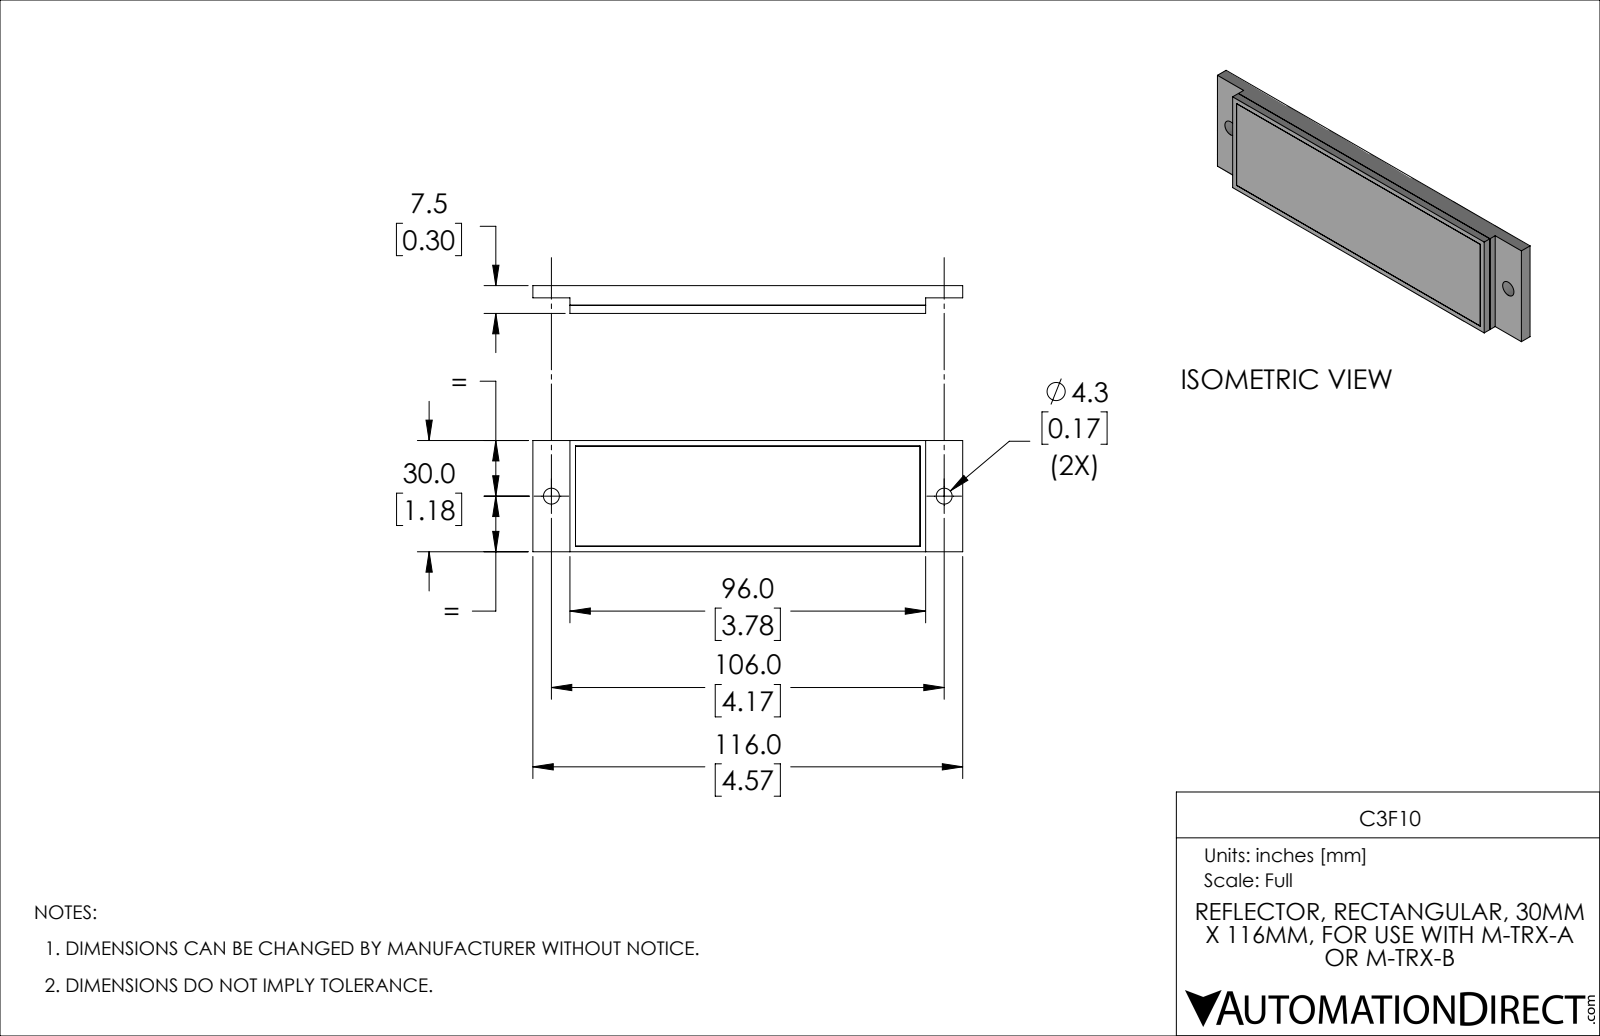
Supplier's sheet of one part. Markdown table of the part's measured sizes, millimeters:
| quantity | value |
| --- | --- |
| part name | C3F10 |
| STEP written by | SolidWorks 2019 (AUTOMOTIVE_DESIGN) |
| units | millimeters |
| bodies | 2 solids, 28 faces (26 planar, 2 cylindrical, 0 other) |
| overall size | 116 × 30 × 7.5 |
| volume | 23 484 mm³ |
| surface area | 15 013 mm² |
| round holes (diameter × count) | 4.3 × 2 |
| main face-to-face distances | 5.3, 7.5, 2.2, 30, 3.3, 2, 4.2, 1.5, 10, 106 |
| hole center spacings | 106 |
